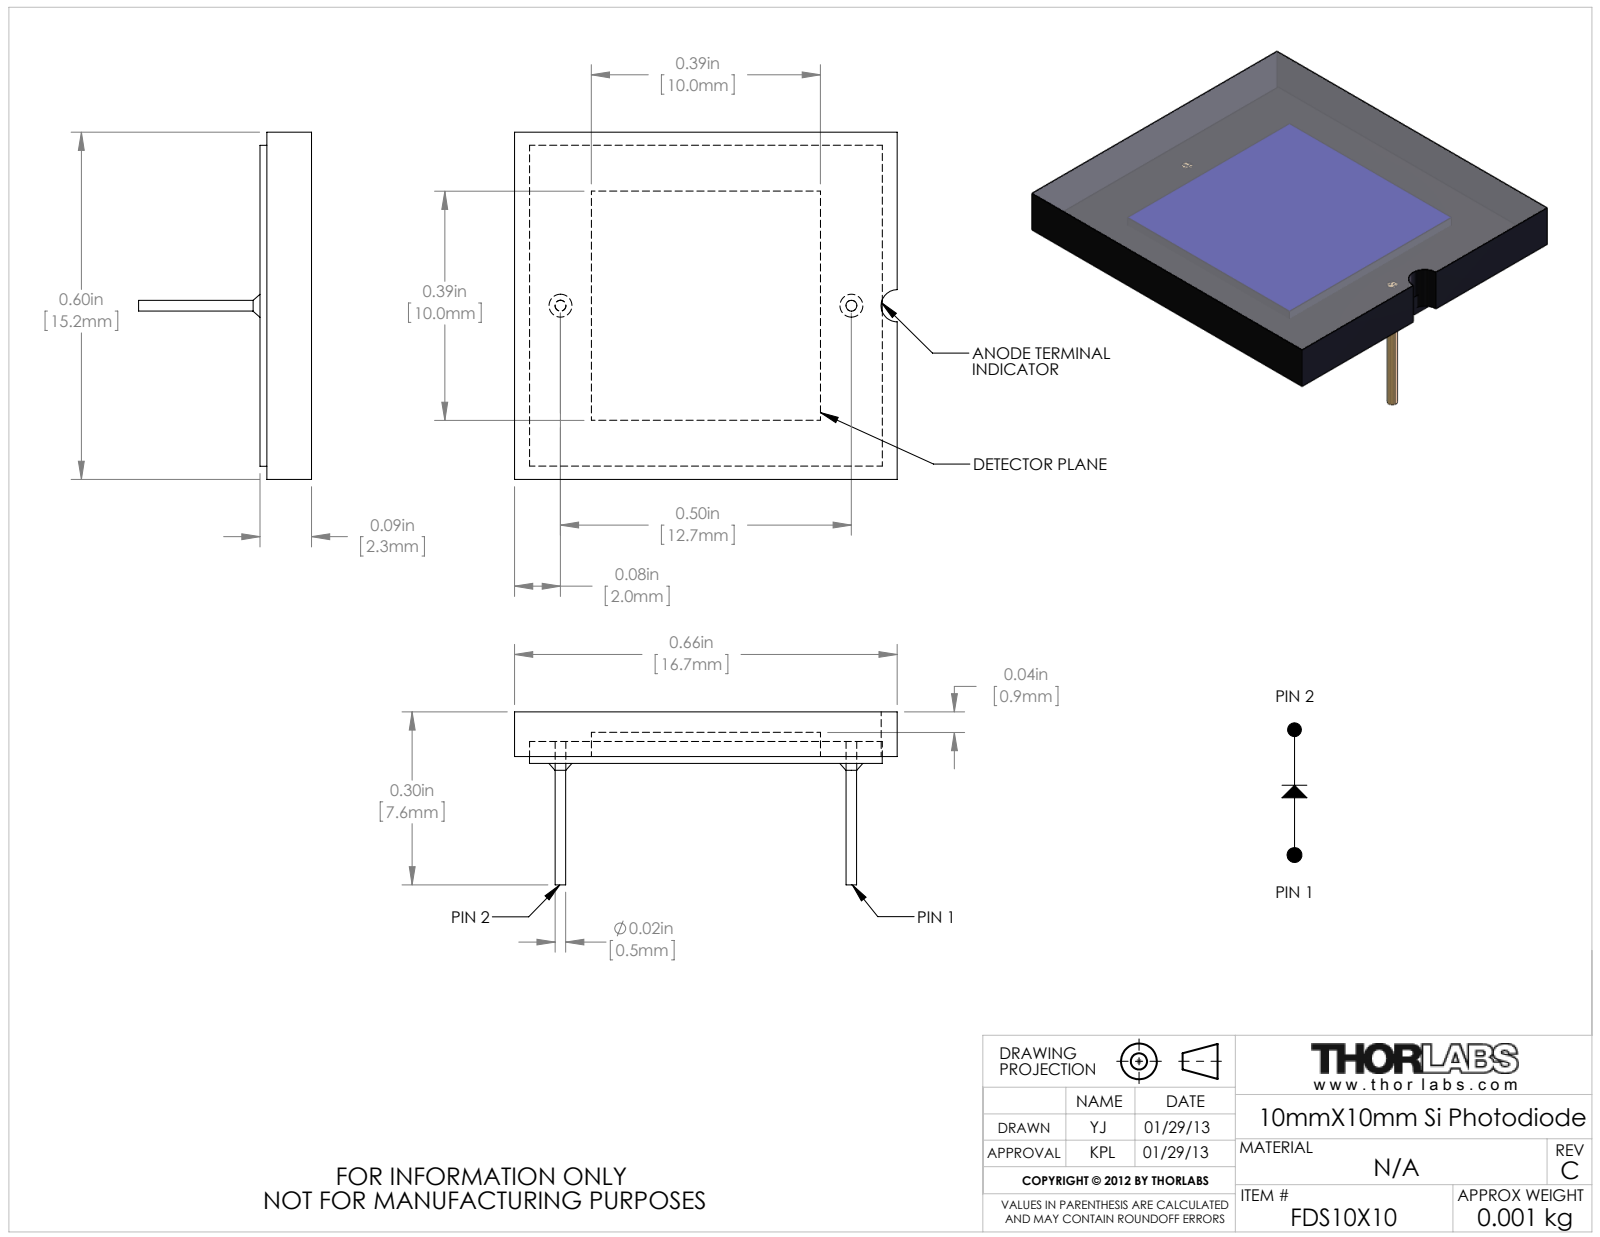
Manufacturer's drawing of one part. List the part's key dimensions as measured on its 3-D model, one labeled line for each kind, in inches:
Part name (STEP PRODUCT): 24706-E01
STEP written by: SolidWorks 2014 (CONFIG_CONTROL_DESIGN)
Units: inches
Bodies: 5 solids, 34 faces (25 planar, 5 cylindrical, 4 other)
Overall size (bounding box): 0.657 × 0.596 × 0.297
Volume: 0.049 in³ · Surface area: 2.137 in²
Round bosses / shafts (diameter × count): ⌀0.019 ×2
Partial cylindrical surfaces — rounded edges, fillets, slot ends (radius × count): R0.028 ×1
Main face-to-face distances: 0.077, 0.026, 0.051, 0.037, 0.089, 0.053, 0.041, 0.016, 0.035, 0.596
